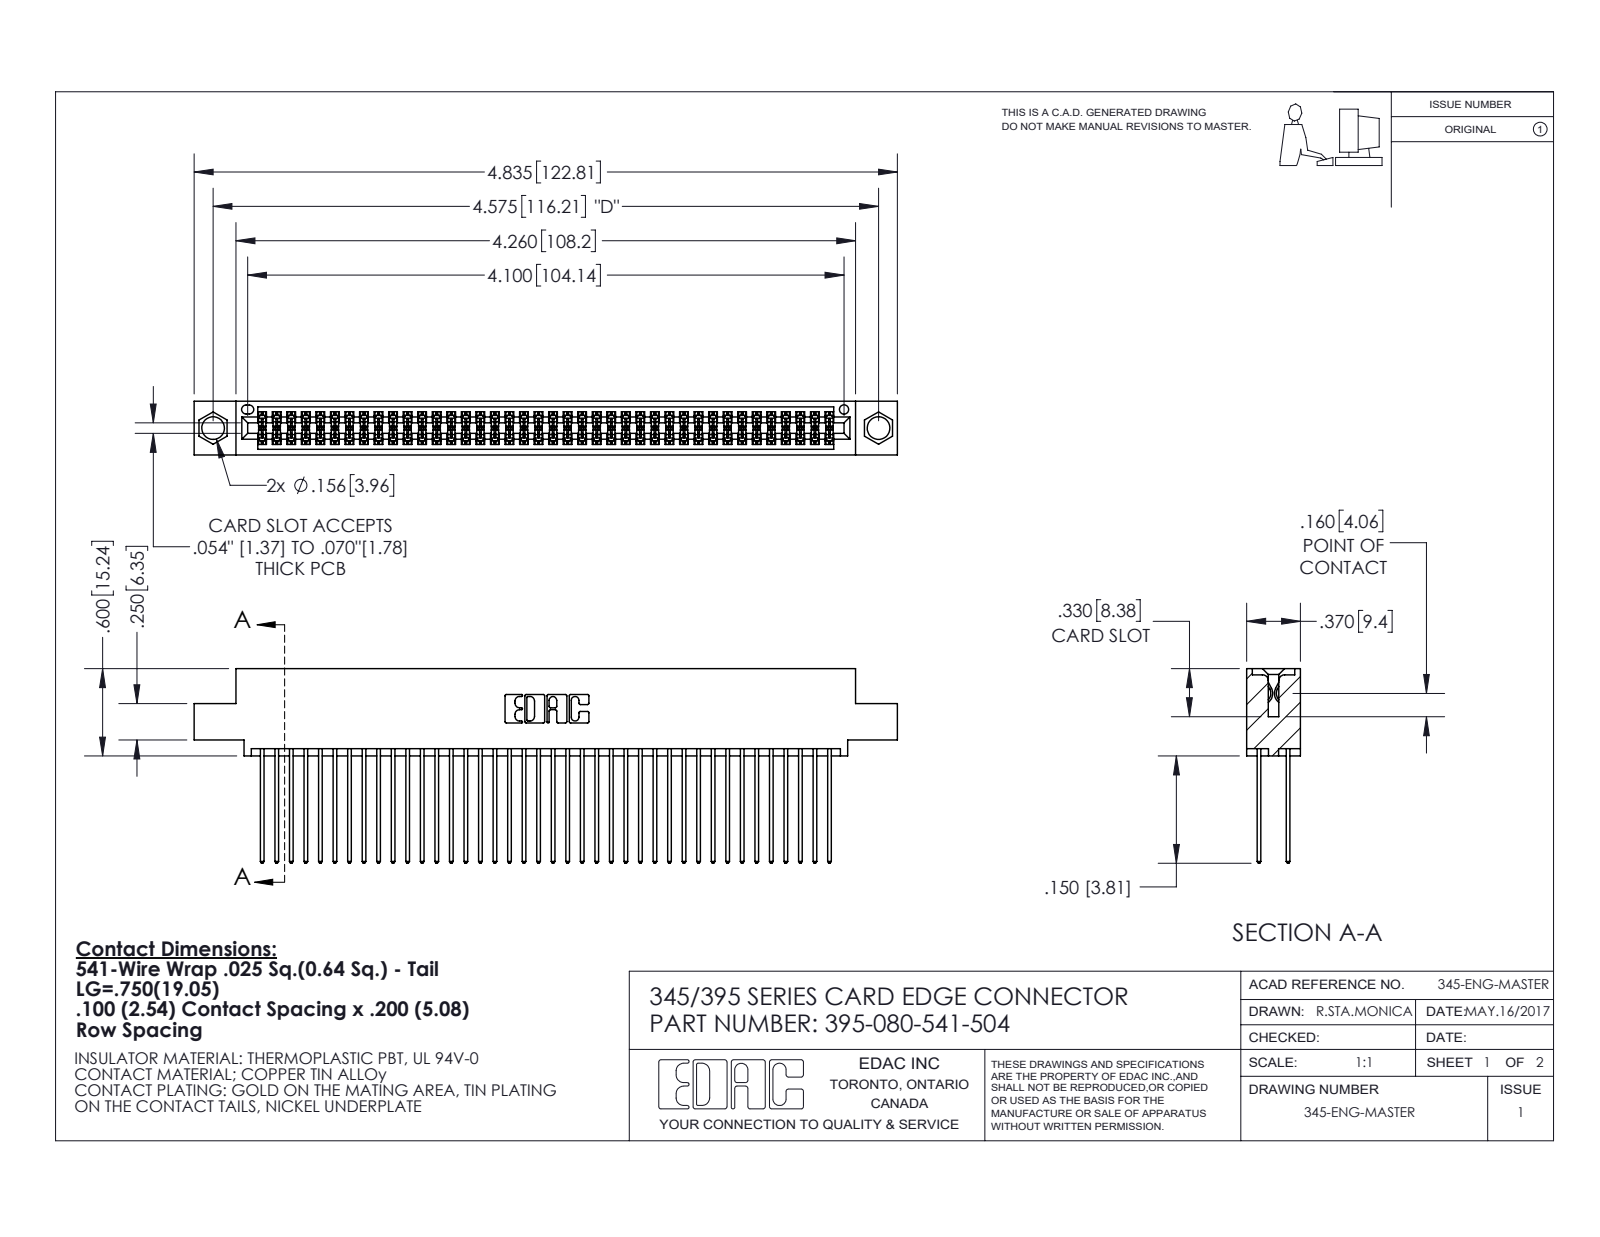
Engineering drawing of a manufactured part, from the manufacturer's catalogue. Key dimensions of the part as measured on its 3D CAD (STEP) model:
Part name (STEP PRODUCT): 345-292-001_345-293-141; 395-080-541-504; 345 Part_0.110 Offset - 0.156 Dia-TI
STEP written by: SolidWorks 2020 (CONFIG_CONTROL_DESIGN)
Units: inches
Bodies: 81 solids, 4144 faces (2738 planar, 1406 cylindrical, 0 other)
Overall size (bounding box): 4.835 × 1.337 × 0.37
Volume: 0.744 in³ · Surface area: 31.13 in²
Round holes (diameter × count): ⌀0.156 ×2, ⌀0.064 ×1
Partial cylindrical surfaces — rounded edges, fillets, slot ends (radius × count): R0.006 ×120, R0.01 ×80, R0.01 ×22, R0.007 ×6, R0.031 ×6, R0.026 ×3, R0.014 ×2, R0.019 ×2
Main face-to-face distances: 0.298, 0.072, 0.2, 0.098, 0.272, 0.025, 0.225, 0.37, 0.175, 0.149
Hole centre spacings: 0.27, 4.339, 4.575
